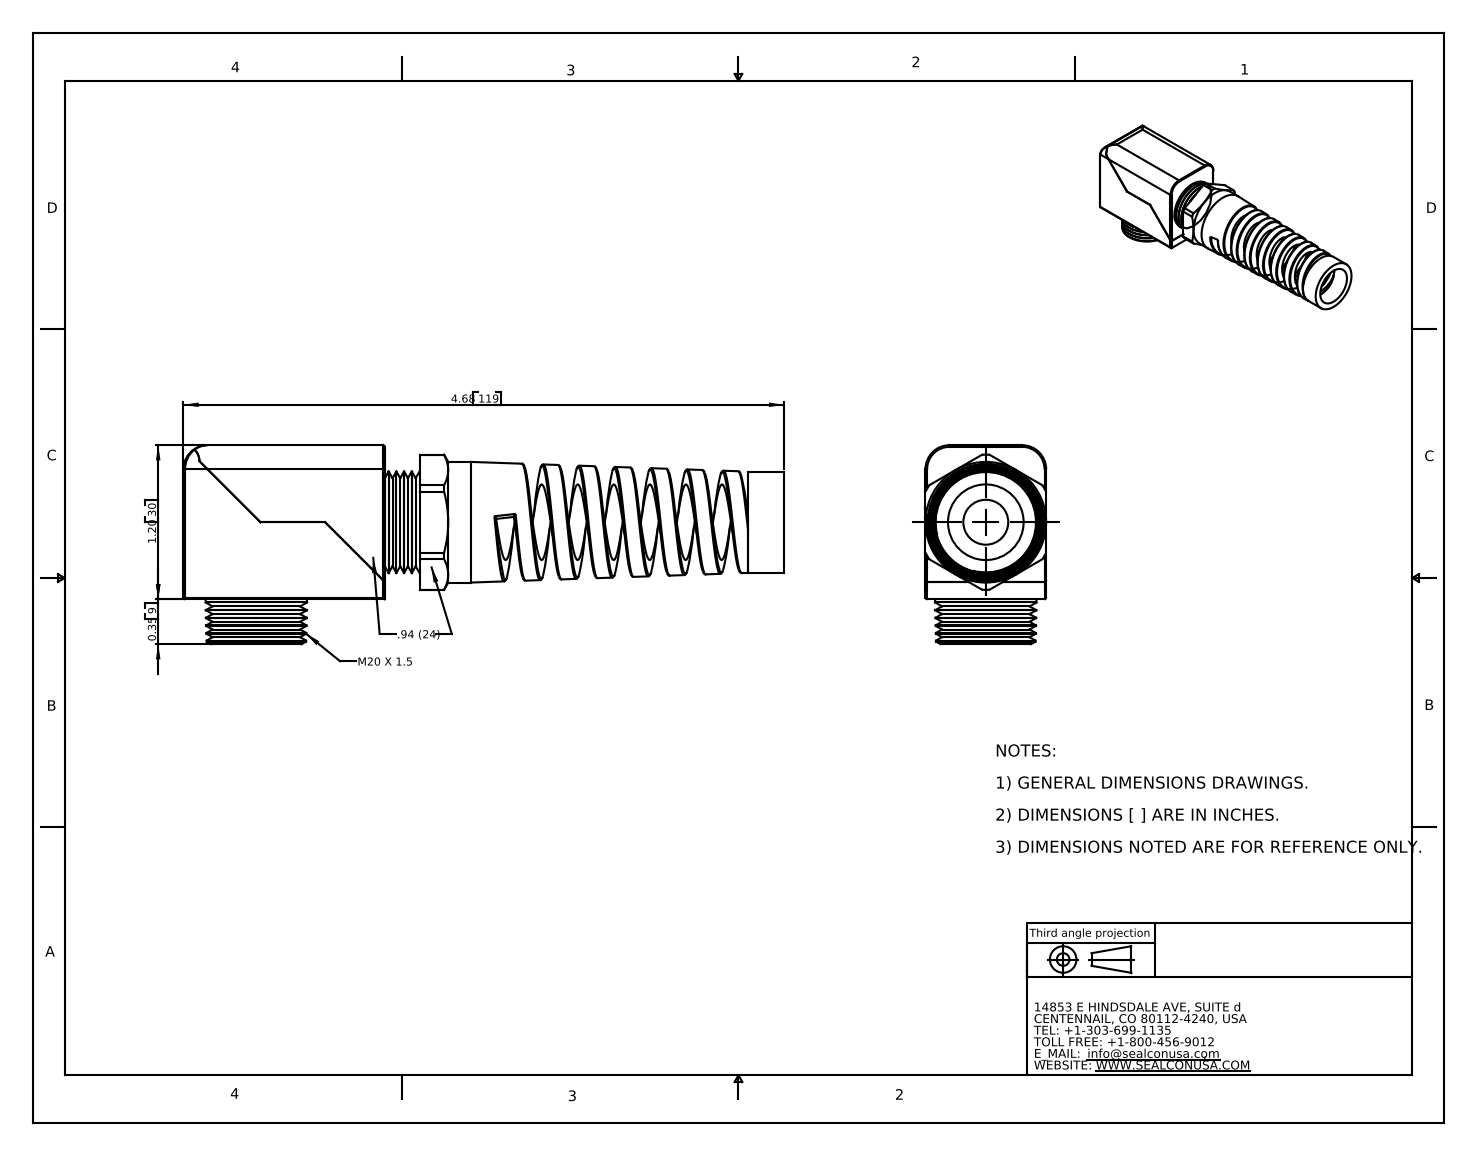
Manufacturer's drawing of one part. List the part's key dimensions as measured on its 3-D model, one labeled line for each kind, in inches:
Part name (STEP PRODUCT): EF20MR-BK
STEP written by: SolidWorks 2007 (CONFIG_CONTROL_DESIGN)
Units: inches
Bodies: 3 solids, 183 faces (31 planar, 63 cylindrical, 89 other)
Overall size (bounding box): 4.68 × 1.55 × 0.94
Volume: 2.449 in³ · Surface area: 29.85 in²
Round holes (diameter × count): ⌀0.35 ×2, ⌀0.589 ×1, ⌀0.632 ×1
Round bosses / shafts (diameter × count): ⌀0.94 ×1, ⌀0.79 ×1, ⌀0.789 ×1
Partial cylindrical surfaces — rounded edges, fillets, slot ends (radius × count): R0.013 ×8, R0.187 ×3, R0.124 ×1, R0.526 ×1
Main face-to-face distances: 0.94, 0.6, 0.356, 1.2, 1.568, 2.831, 4.399, 2.56, 0.271, 1.839
